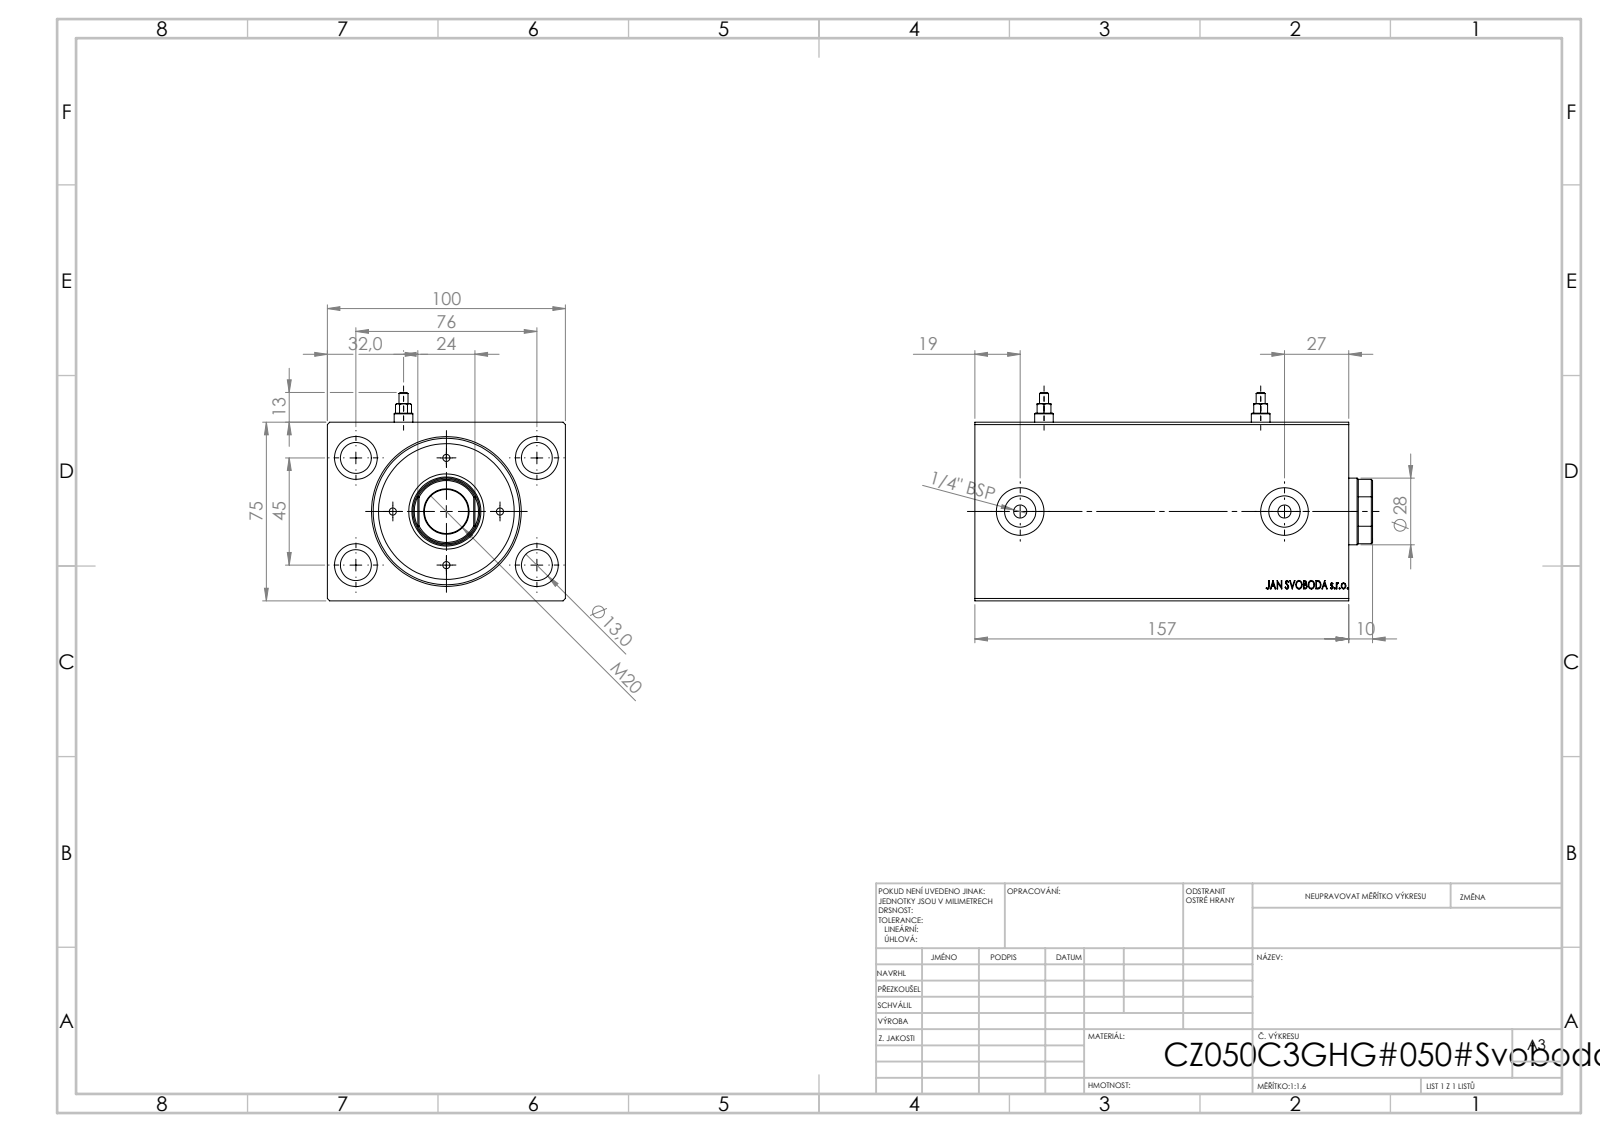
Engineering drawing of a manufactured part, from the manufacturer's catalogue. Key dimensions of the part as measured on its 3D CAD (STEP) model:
STEP written by: SolidWorks 2019 (CONFIG_CONTROL_DESIGN)
Units: millimetres
Bodies: 1 solid, 825 faces (397 planar, 46 cylindrical, 382 other)
Overall size (bounding box): 157 × 100 × 75
Volume: 795 949 mm³ · Surface area: 119 204 mm²
Round holes (diameter × count): ⌀13 ×4, ⌀18 ×4, ⌀5.5 ×2, ⌀8 ×2, ⌀13.16 ×2, ⌀20 ×2, ⌀36 ×1, ⌀50 ×1, ⌀61.5 ×1
Main face-to-face distances: 75, 100, 157, 139.2, 17.8, 156.8, 17.6, 10, 129.2, 146.8
Hole centre spacings: 44.16, 45, 76, 88.32, 91, 111
